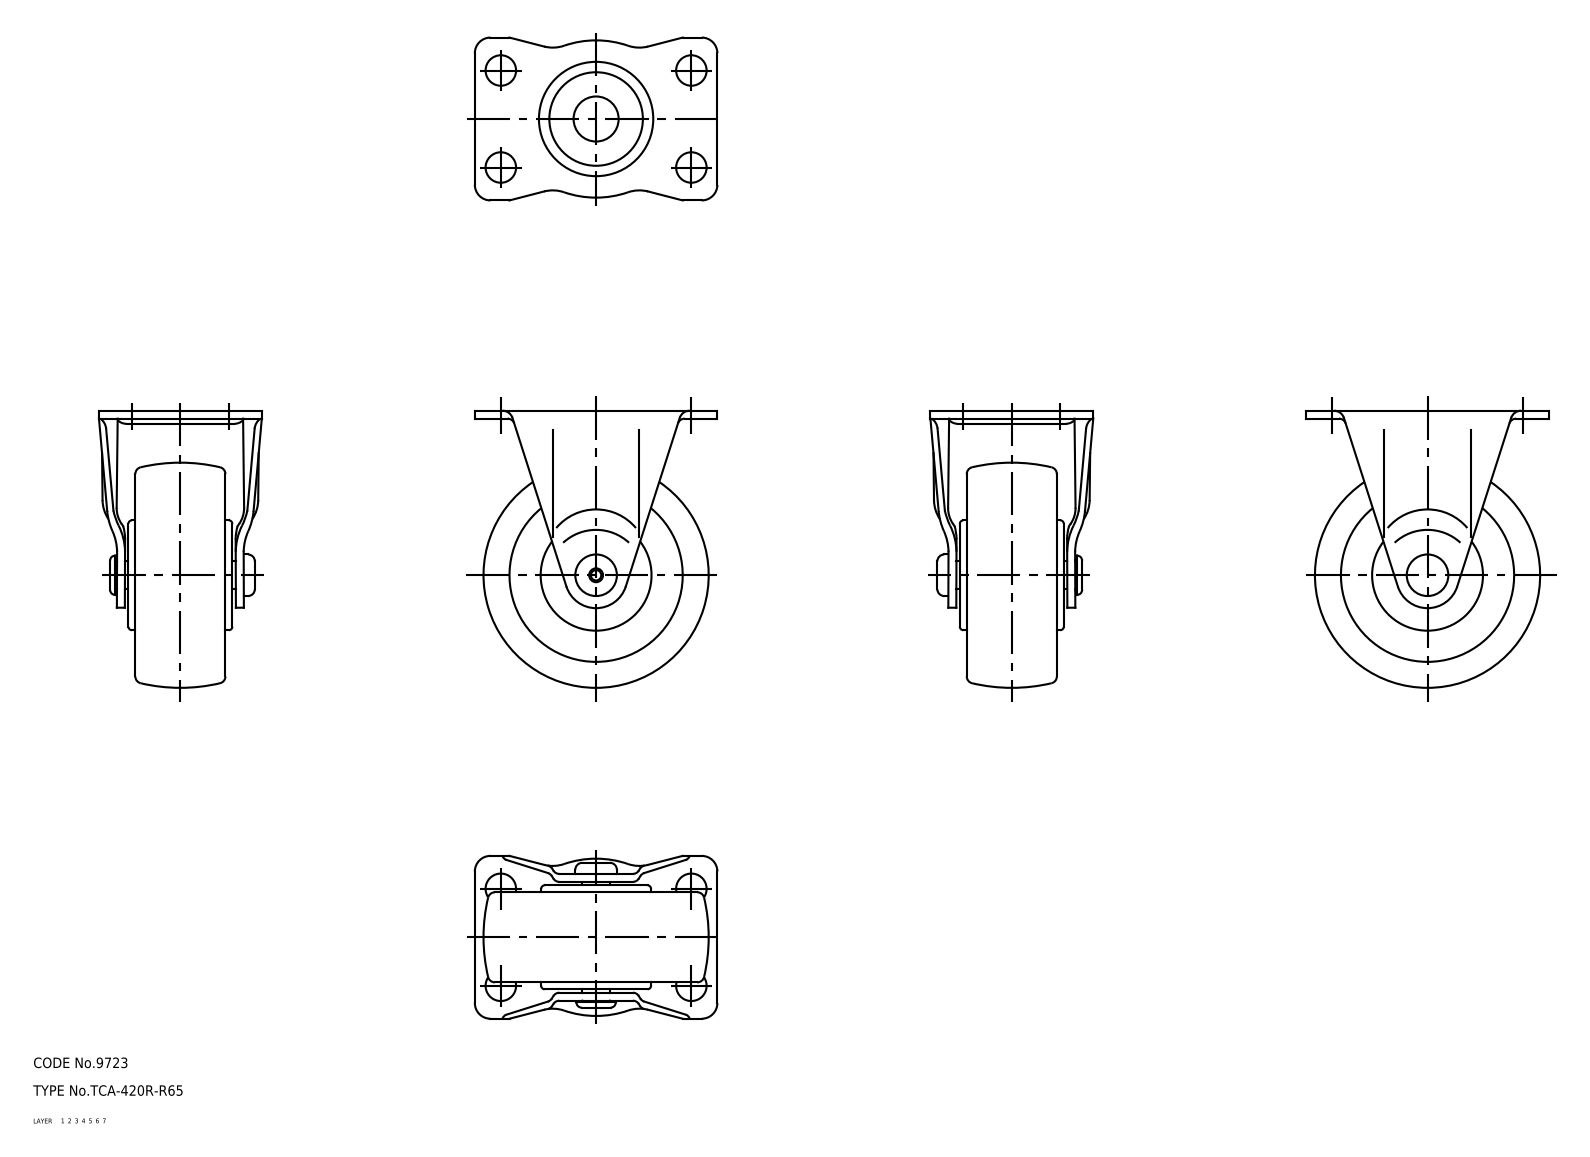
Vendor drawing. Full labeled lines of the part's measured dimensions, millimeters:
Part name (STEP PRODUCT): wheel; axle; No_420_R_R65_5_13580_36
STEP written by: CADfix (AUTOMOTIVE_DESIGN)
Units: millimetres
Bodies: 3 solids, 174 faces (0 planar, 0 cylindrical, 174 other)
Overall size (bounding box): 80 × 70 × 47
Volume: 98 848 mm³ · Surface area: 27 374 mm²
